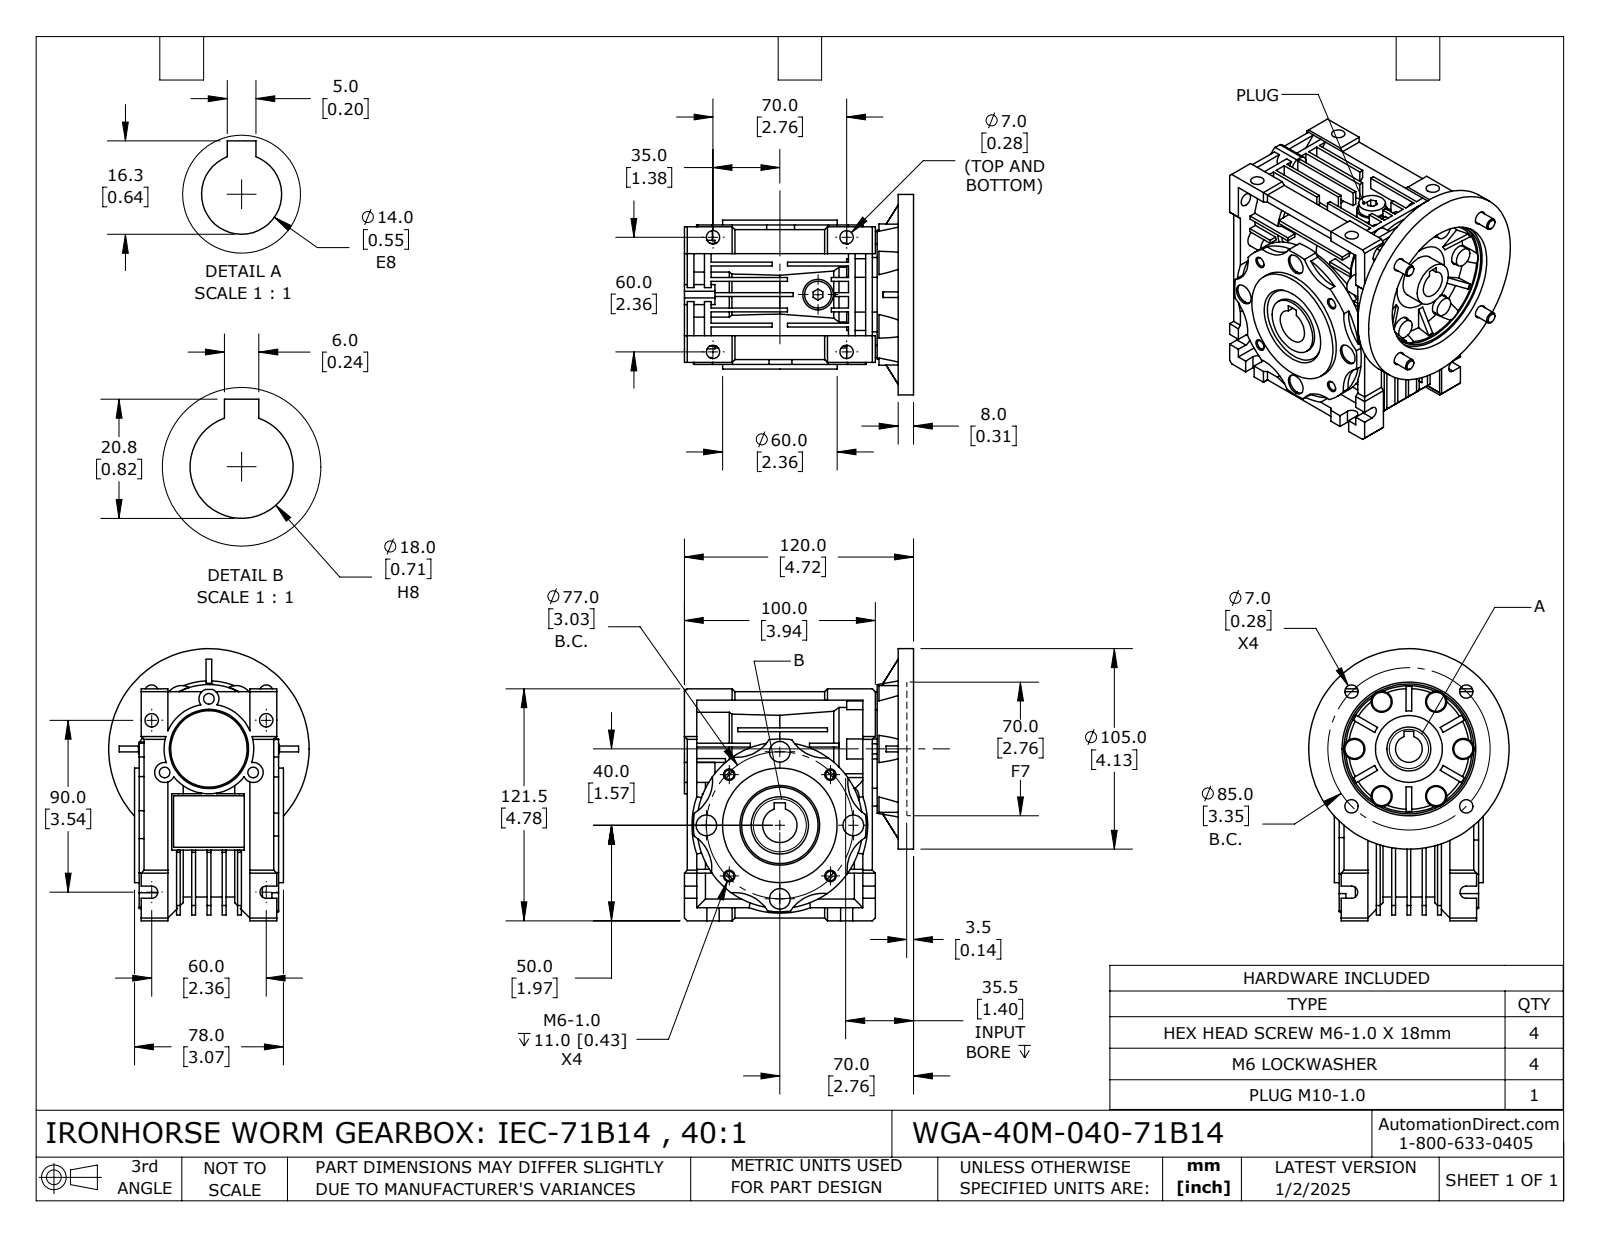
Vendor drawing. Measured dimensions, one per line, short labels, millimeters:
name: WGA-40M-040-71B14
written by: SolidWorks 2024 (CONFIG_CONTROL_DESIGN)
unit: mm
bodies: 14 solids, 956 faces (550 planar, 281 cylindrical, 125 other)
size: 142.5 × 128.5 × 105
volume: 688 964 mm³; area: 170 588 mm²
holes: 10× ⌀7, 6× ⌀11, 4× ⌀4.92, 4× ⌀6.1, 4× ⌀10.8, 3× ⌀5.55, 1× ⌀9, 1× ⌀14, 1× ⌀15, 1× ⌀18, 1× ⌀23, 1× ⌀28
bosses: 6× ⌀10, 4× ⌀12.2, 4× ⌀6, 1× ⌀105, 1× ⌀75, 1× ⌀60, 1× ⌀54, 1× ⌀47
rounds: 8× R20, 6× R3.2, 6× R5.22, 6× R8.5, 3× R5.25, 1× R34.31, 1× R43.5, 1× R43.59
face distances: 8, 6, 2, 1.5, 16, 10, 5, 11, 2.5, 24
hole spacings: 28.5, 29.1, 70.22, 49.36, 16.69, 30.09, 33.54, 37.5
